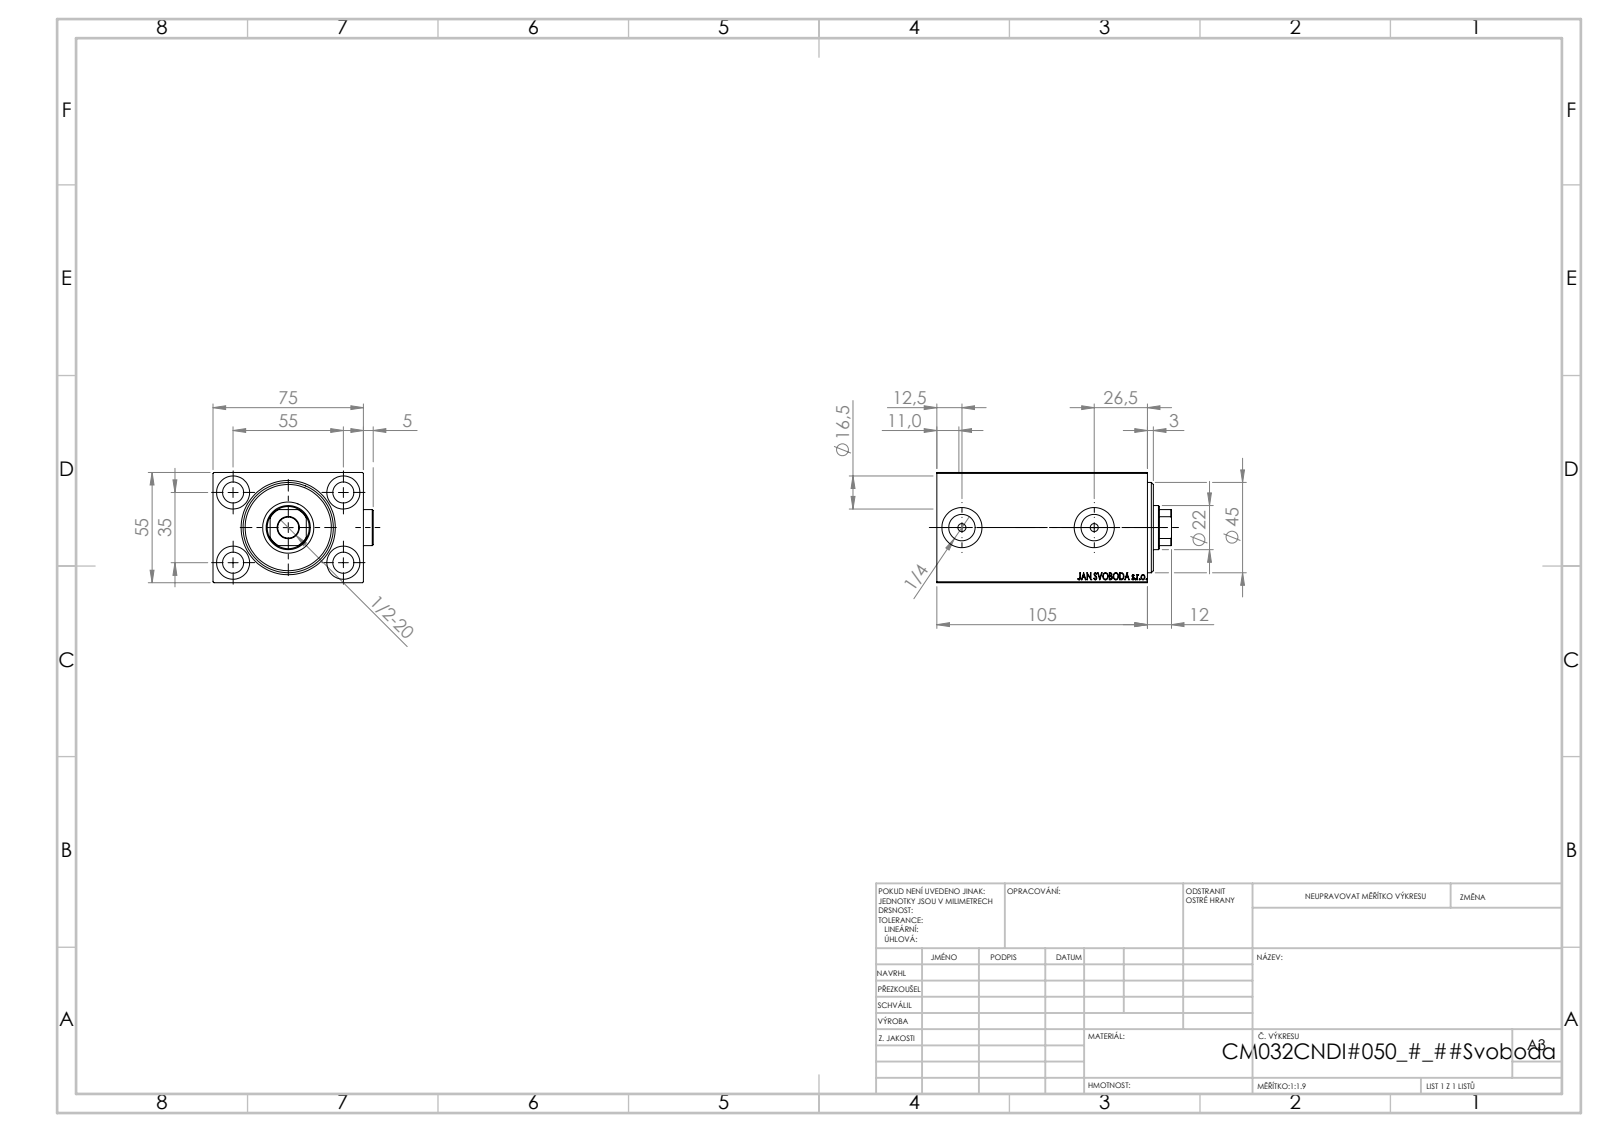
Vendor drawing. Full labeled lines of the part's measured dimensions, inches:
Part name (STEP PRODUCT): V450CM_C_VCP; V450CM_VC_B; Zatka_OIL_PORT; V450CM_C_Body
STEP written by: SolidWorks 2019 (CONFIG_CONTROL_DESIGN)
Units: inches
Bodies: 5 solids, 916 faces (442 planar, 76 cylindrical, 398 other)
Overall size (bounding box): 4.606 × 3.146 × 2.165
Volume: 22.26 in³ · Surface area: 124.2 in²
Round holes (diameter × count): ⌀0.413 ×5, ⌀0.65 ×4, ⌀0.157 ×2, ⌀0.518 ×2, ⌀0.787 ×2, ⌀0.866 ×1, ⌀1.004 ×1, ⌀1.26 ×1, ⌀1.339 ×1, ⌀1.772 ×1
Round bosses / shafts (diameter × count): ⌀0.709 ×2
Partial cylindrical surfaces — rounded edges, fillets, slot ends (radius × count): R0.413 ×1
Main face-to-face distances: 2.165, 2.953, 0.197, 0.394, 3.74, 4.134, 3.937, 3.543, 2.949, 3.268
Hole centre spacings: 1.283, 1.378, 2.165, 2.567, 2.598
